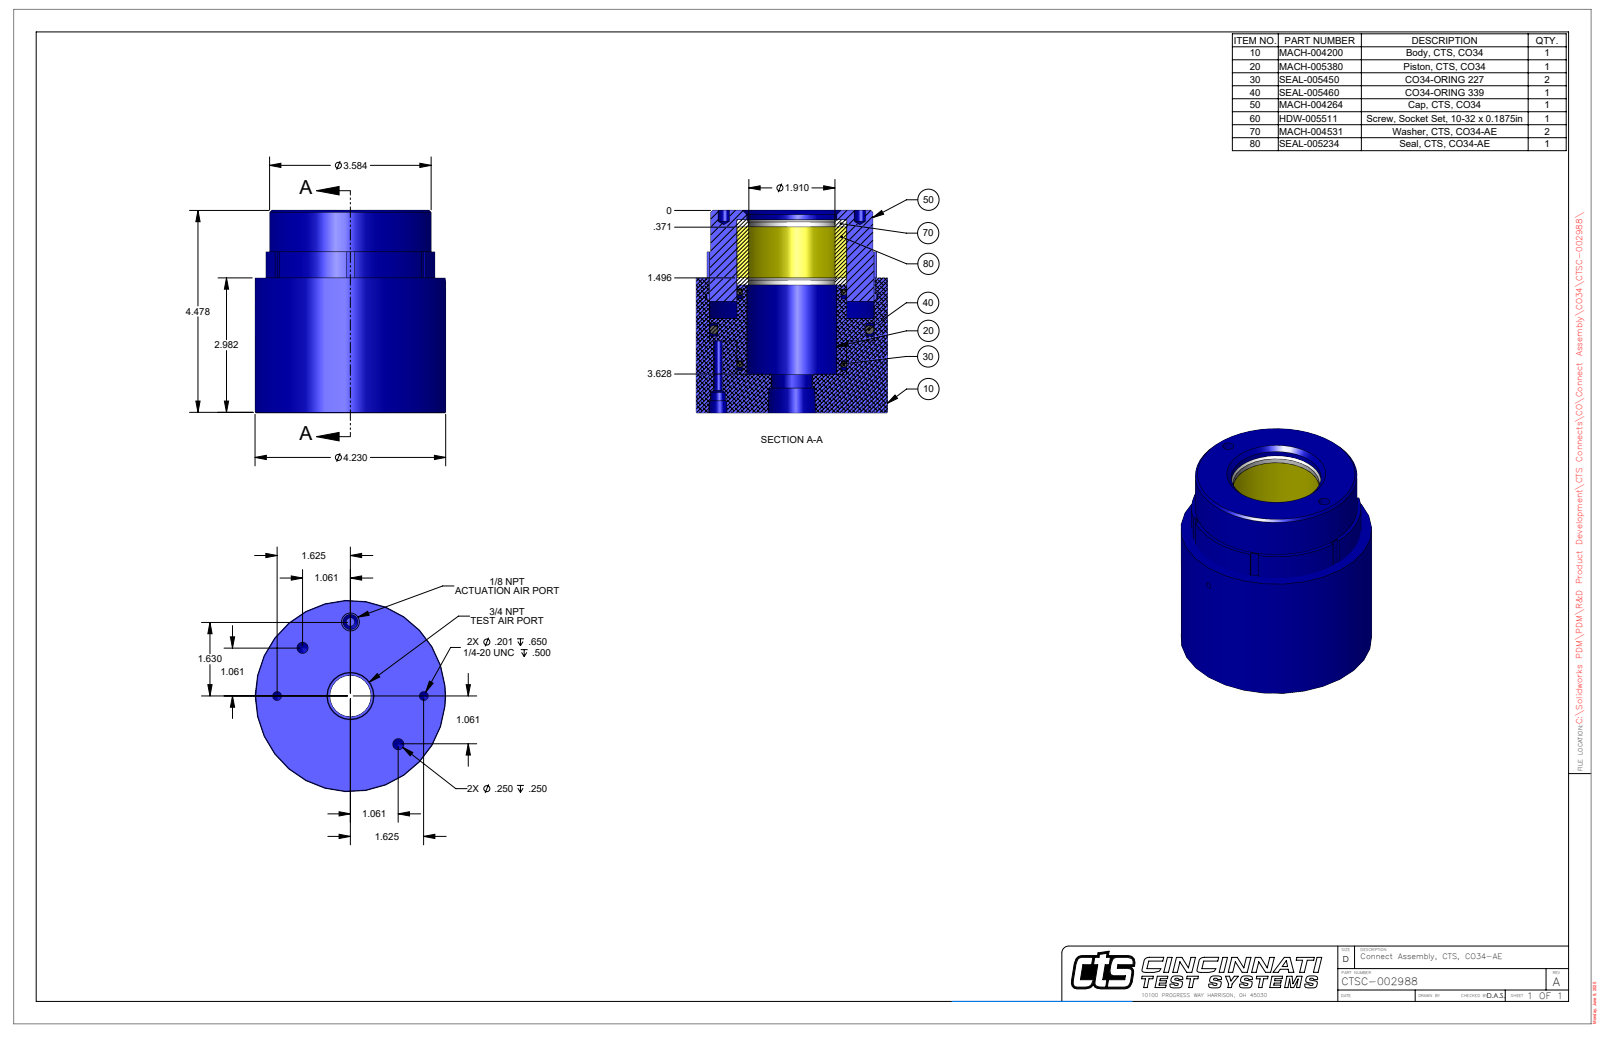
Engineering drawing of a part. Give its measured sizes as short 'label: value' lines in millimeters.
name: CTSC-002988
written by: SolidWorks 2023 (AUTOMOTIVE_DESIGN)
unit: mm
bodies: 1 solid, 129 faces (47 planar, 56 cylindrical, 26 other)
size: 113.7 × 107.5 × 107.4
volume: 749 400 mm³; area: 73 030 mm²
holes: 4× ⌀6.4, 2× ⌀5.1, 1× ⌀3.2, 1× ⌀4, 1× ⌀4.7, 1× ⌀8.4, 1× ⌀23, 1× ⌀48.5, 1× ⌀48.6, 1× ⌀50.5, 1× ⌀50.5, 1× ⌀61.6
bosses: 1× ⌀107.4, 1× ⌀95.3, 1× ⌀91, 1× ⌀61.4
rounds: 1× R46.8, 1× R53.4
face distances: 113.7, 75.7, 38, 21.6, 54.2, 92.2, 90.4, 68.8, 14.6, 23.4
hole spacings: 38.1, 56.2, 29.2, 30.5, 41.3, 58.5, 70.4, 73.3
